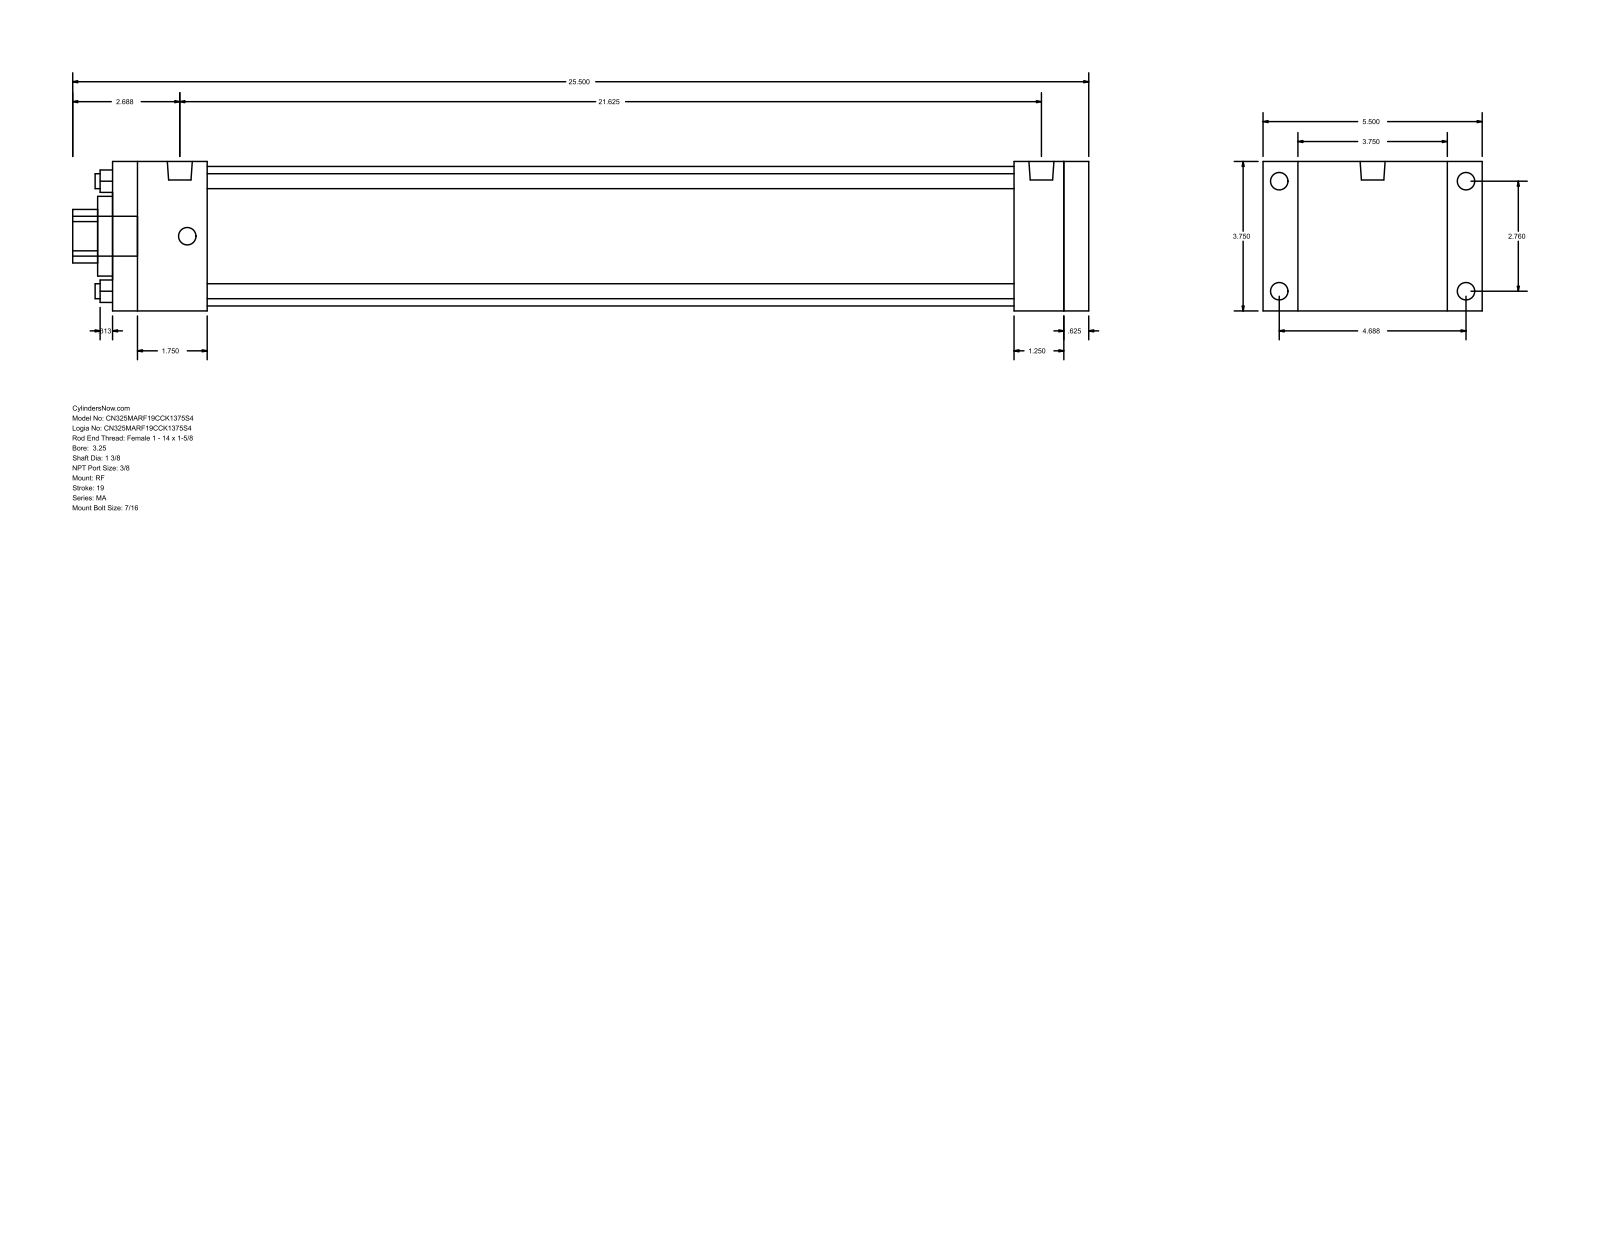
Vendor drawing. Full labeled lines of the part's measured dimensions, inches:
Part name (STEP PRODUCT): MA_RF__0325_1.375
STEP written by: GSSL Pune (CONFIG_CONTROL_DESIGN)
Units: inches
Bodies: 0 solids, 92 faces (64 planar, 28 cylindrical, 0 other)
Overall size (bounding box): 25.5 × 5.5 × 3.75
Round holes (diameter × count): ⌀0.375 ×4, ⌀1.375 ×1, ⌀2 ×1, ⌀3.5 ×1
Round bosses / shafts (diameter × count): ⌀0.437 ×8, ⌀0.627 ×2, ⌀1 ×1
Partial cylindrical surfaces — rounded edges, fillets, slot ends (radius × count): R0.672 ×1
Main face-to-face distances: 3.75, 24.5, 0.625, 23.875, 0.875, 4.625, 22.625, 1.25, 1.875, 2.375
Hole centre spacings: 1.952, 2.76, 3.903
